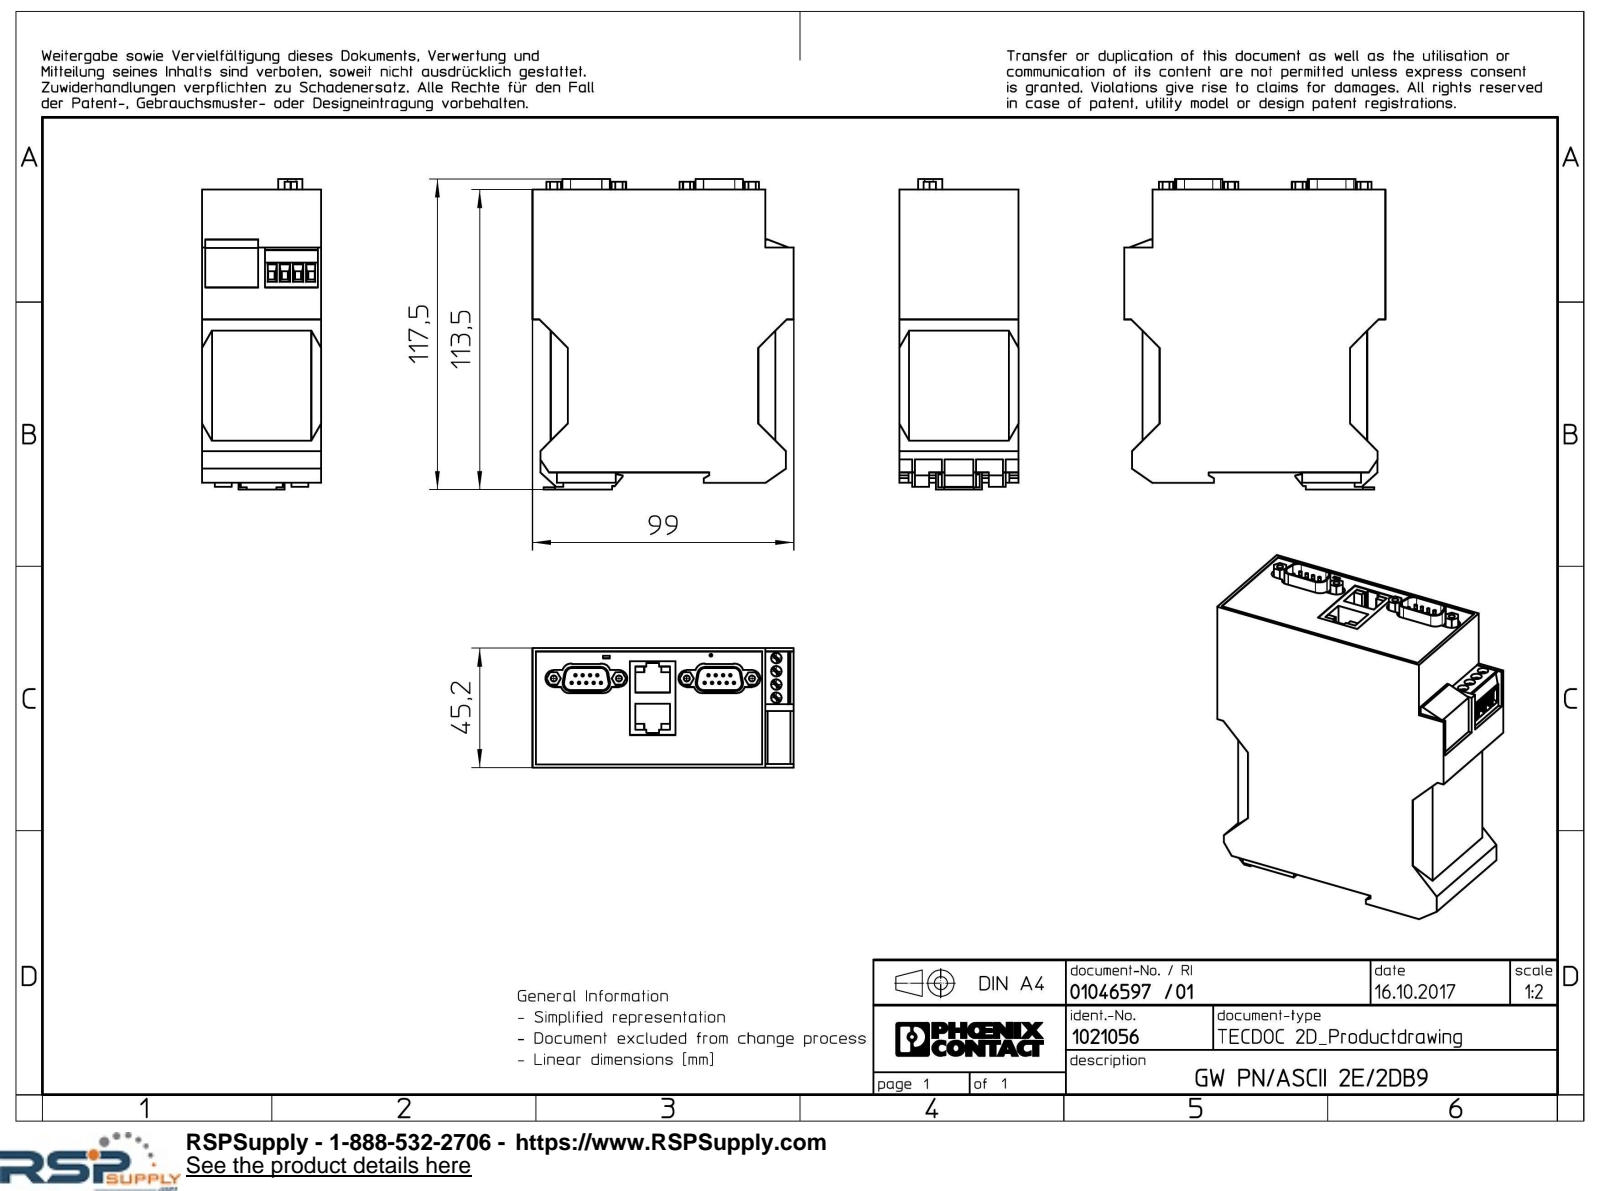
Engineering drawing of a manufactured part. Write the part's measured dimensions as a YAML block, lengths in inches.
part_name: "GW...ASCII_2E_2DB9-select"
step_written_by: "Creo Elements/Direct Modeling 18.1I 14-Aug-2016 (C) Parametric Technology GmbH (AUTOMOTIVE_DESIGN)"
units: inches
bodies: {solids: 1, faces: 412, planar: 330, cylindrical: 82, other: 0}
overall_size: [4.626, 3.898, 1.78]
volume: 26.7
surface_area: 67.45
round_holes:
  - {diameter: 0.09, count: 4}
  - {diameter: 0.157, count: 4}
  - {diameter: 0.043, count: 1}
round_bosses_or_shafts:
  - {diameter: 0.039, count: 18}
partial_cylinders:
  - {radius: 0.125, count: 12}
  - {radius: 0.1, count: 8}
  - {radius: 0.12, count: 8}
face_to_face_distances: [1.78, 3.624, 0.274, 0.157, 4.205, 3.35, 4.362, 0.148, 3.476, 3.203]
hole_center_spacings: [0.197, 0.394, 0.974, 1.984, 0.373, 0.378, 0.462, 0.473]
